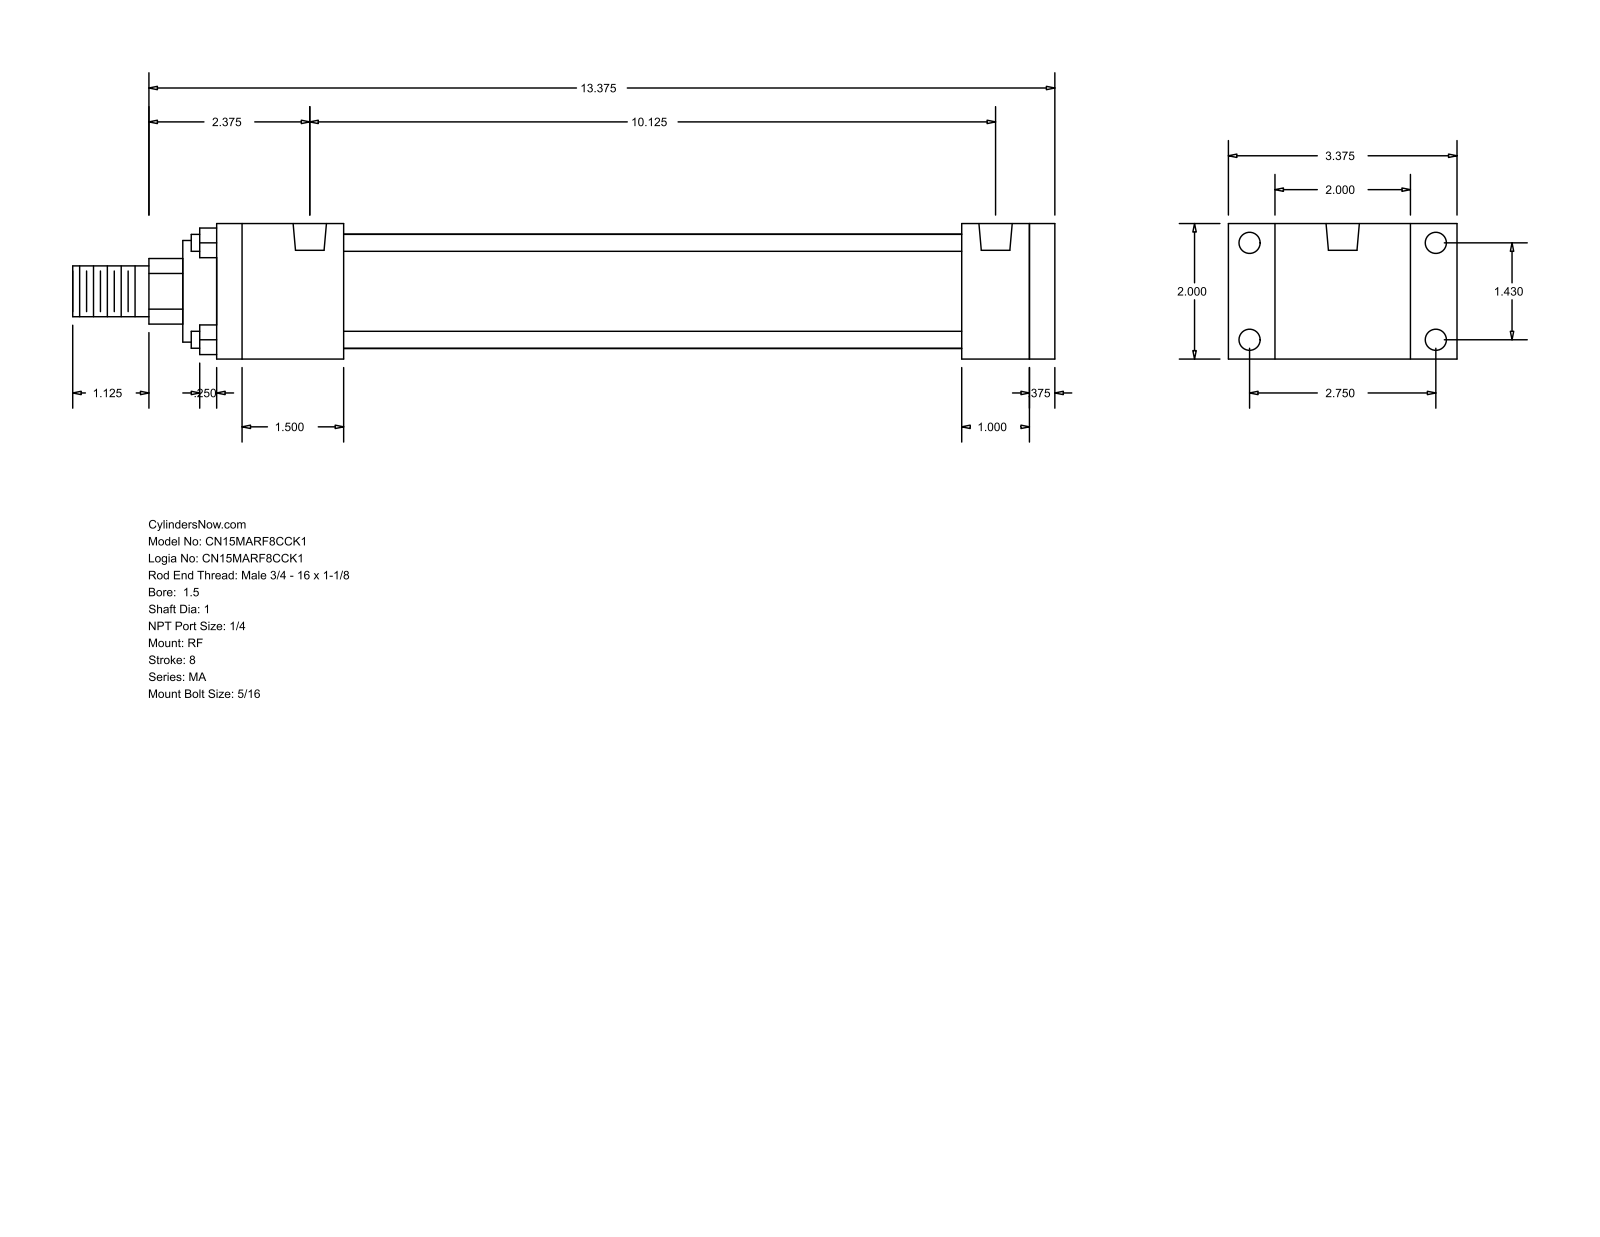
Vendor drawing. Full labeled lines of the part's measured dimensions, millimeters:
Part name (STEP PRODUCT): MA_RF__0150_1
STEP written by: GSSL Pune (CONFIG_CONTROL_DESIGN)
Units: millimetres
Bodies: 0 solids, 92 faces (64 planar, 28 cylindrical, 0 other)
Overall size (bounding box): 368.3 × 85.72 × 50.8
Round holes (diameter × count): ⌀7.94 ×8, ⌀12.49 ×2
Round bosses / shafts (diameter × count): ⌀6.35 ×4, ⌀42.93 ×1, ⌀38.1 ×1, ⌀25.4 ×1, ⌀19.05 ×1
Partial cylindrical surfaces — rounded edges, fillets, slot ends (radius × count): R12.29 ×1
Main face-to-face distances: 50.8, 9.53, 304.8, 25.4, 314.33, 279.4, 34.93, 47.63, 231.77, 257.17
Hole centre spacings: 36.32, 69.84, 78.72, 257.17
